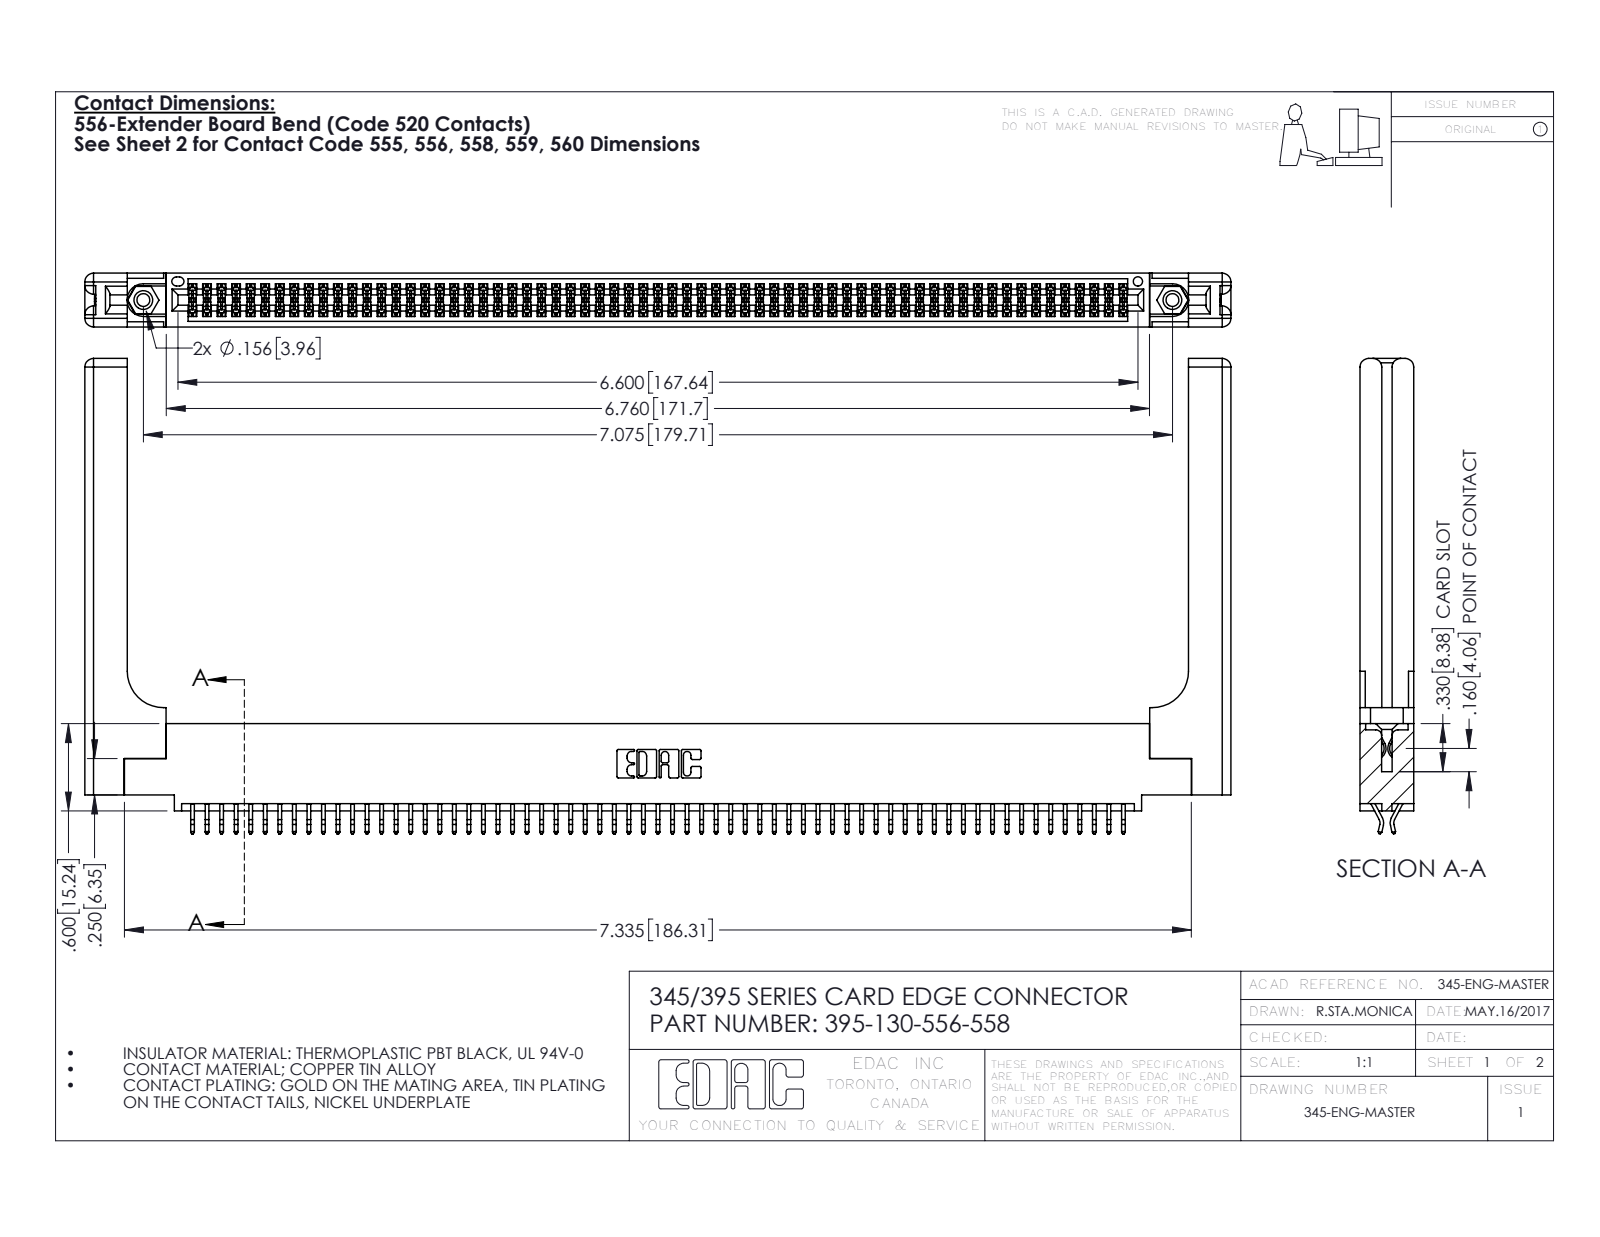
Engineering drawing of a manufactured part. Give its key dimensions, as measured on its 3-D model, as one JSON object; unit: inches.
{"part_name": "345-220-058_345-220-058; 345-250-001_345-250-001-102; 395-130-556-558; 345-292-001_556 Tail (+1 more)", "step_written_by": "SolidWorks 2016 (CONFIG_CONTROL_DESIGN)", "units": "inches", "bodies": {"solids": 135, "faces": 7666, "planar": 5042, "cylindrical": 2564, "other": 60}, "overall_size": [7.879, 3.267, 0.37], "volume_in3": 1.712, "surface_area_in2": 53.35, "round_holes": [[0.089, 2], [0.125, 2], [0.156, 2], [0.064, 1]], "round_bosses_or_shafts": [[0.155, 2]], "partial_cylinders_radius": [[0.006, 195], [0.01, 22], [0.06, 16], [0.007, 6], [0.031, 6], [0.026, 3], [0.01, 2], [0.014, 2]], "face_to_face_distances": [0.072, 0.298, 0.37, 0.025, 0.098, 0.272, 0.2, 0.225, 0.148, 0.15], "hole_center_spacings": [0.27, 6.839, 7.075]}
